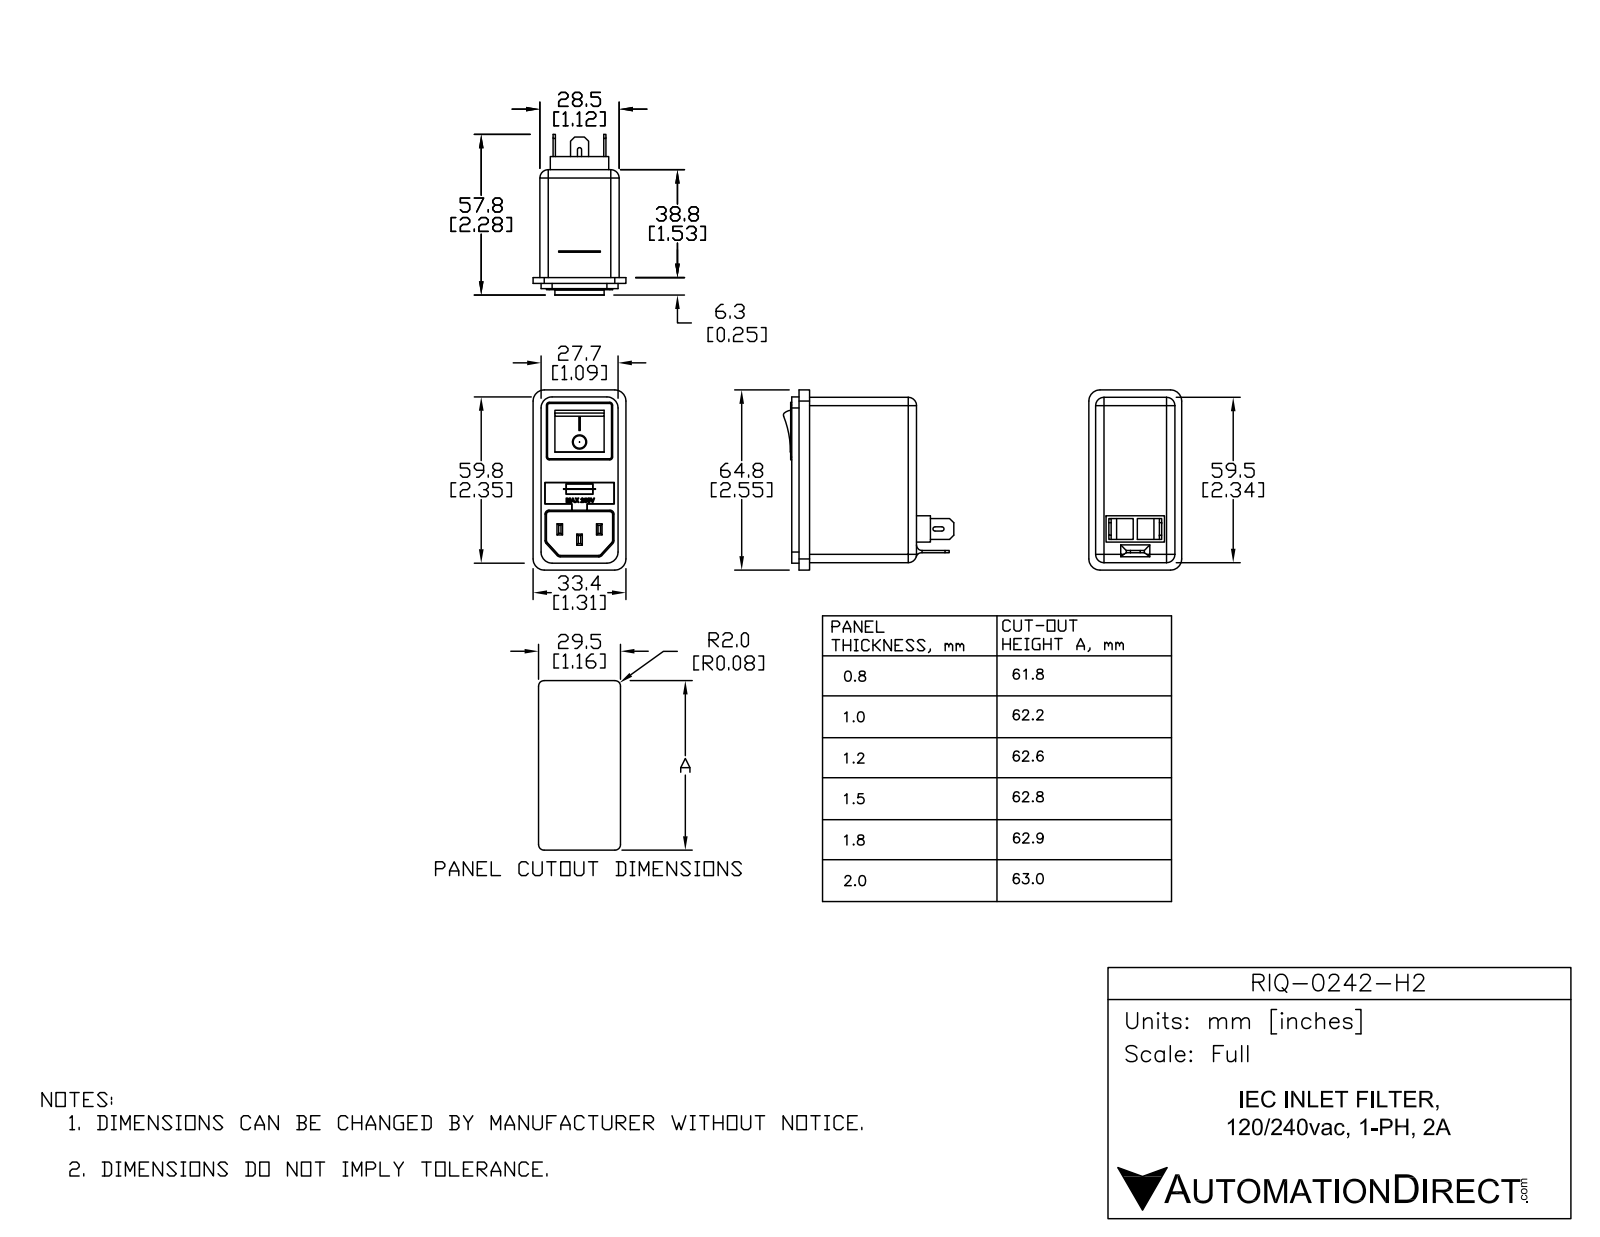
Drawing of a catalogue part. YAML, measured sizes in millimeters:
part_name: "RIQ0242H2"
step_written_by: "SolidWorks 2015 (AUTOMOTIVE_DESIGN)"
units: millimeters
bodies: {solids: 5, faces: 397, planar: 282, cylindrical: 72, other: 43}
overall_size: [64.8, 61.48, 33.4]
volume: 72707
surface_area: 17741
partial_cylinders:
  - {radius: 0.6, count: 11}
  - {radius: 3, count: 8}
  - {radius: 0.1, count: 6}
  - {radius: 2, count: 5}
  - {radius: 0.15, count: 4}
  - {radius: 0.75, count: 4}
  - {radius: 4, count: 4}
  - {radius: 2.32, count: 2}
face_to_face_distances: [28.5, 0.5, 2.25, 26.25, 0.4, 59.5, 44.9, 2.6, 1.75, 26.75]
